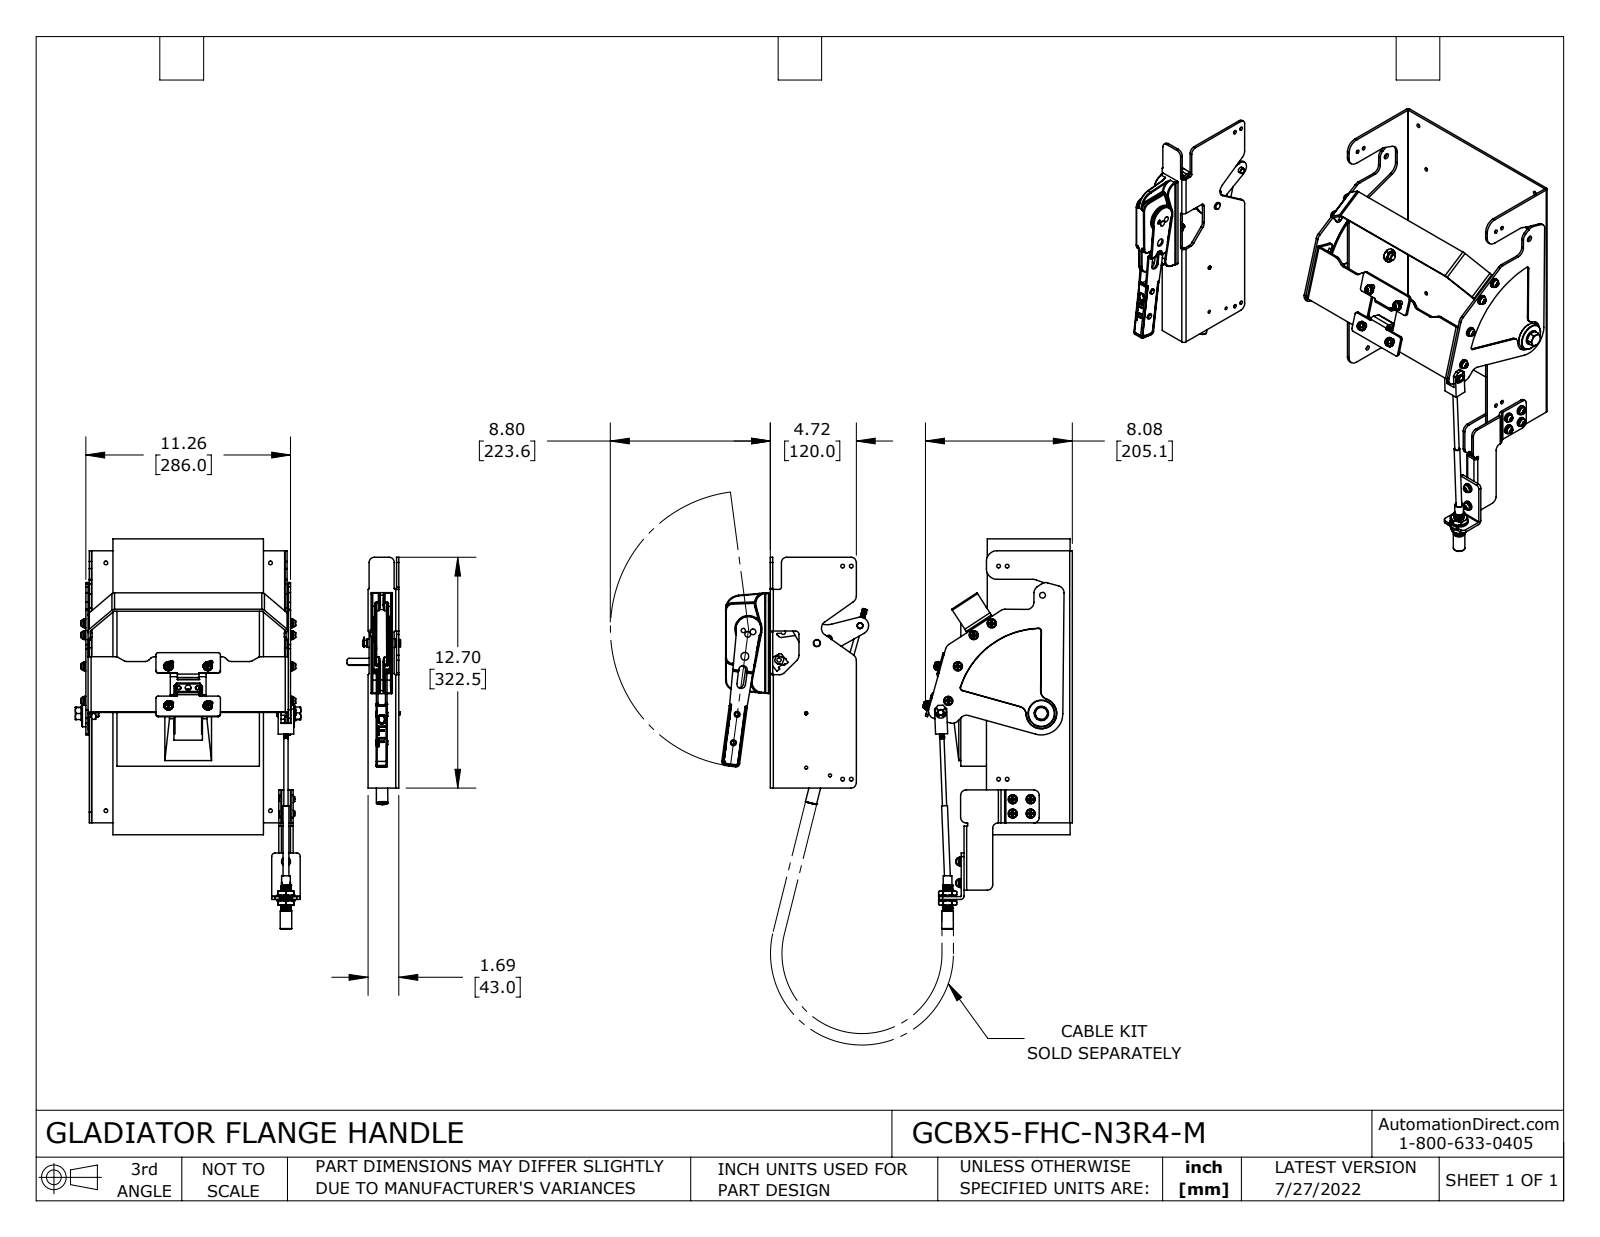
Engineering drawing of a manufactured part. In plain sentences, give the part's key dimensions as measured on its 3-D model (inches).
The part is named "GCBX5-FHC-N3R4-M_MCCB; GCBX5-FHC-N3R4-M_1; GCBX5-FHC-N3R4-M; GCBX5-FHC-N3R4-M_2". Its 3-D file was written by "SolidWorks 2021 (CONFIG_CONTROL_DESIGN)". It is 98 solids with 4613 faces: 1724 planar, 2103 cylindrical and 786 other. Overall it measures 21.437 by 19.273 by 17.887 inches. Its volume is 801.3 cubic inches and its surface area 2 026 square inches. Round holes: 22 of diameter 0.24, 18 of diameter 0.26, 13 of diameter 0.169, 10 of diameter 0.209, 9 of diameter 0.197, 9 of diameter 0.319, 8 of diameter 0.205, 7 of diameter 0.244, 5 of diameter 0.236, 4 of diameter 0.161, 3 of diameter 0.217, 3 of diameter 0.394. Round bosses or shafts: 25 of diameter 0.236, 18 of diameter 0.492, 18 of diameter 0.48, 18 of diameter 0.413, 10 of diameter 0.315, 3 of diameter 0.984, 3 of diameter 0.472, 3 of diameter 0.394. Partial cylindrical surfaces (rounded edges, fillets, slot ends): 204 of radius 0.02, 170 of radius 0.012, 93 of radius 0.039, 44 of radius 0.118, 34 of radius 0.079, 22 of radius 0.295, 21 of radius 0.394, 20 of radius 0.059. The main face-to-face distances are 0.126, 1.307, 9.575, 10.756, 1.181, 9.449, 0.189, 10.945, 16.902, 6.146. The hole center spacings are 0.512, 2.165, 2.707, 3.119, 8.847, 11.001, 13.856, 0.291.
